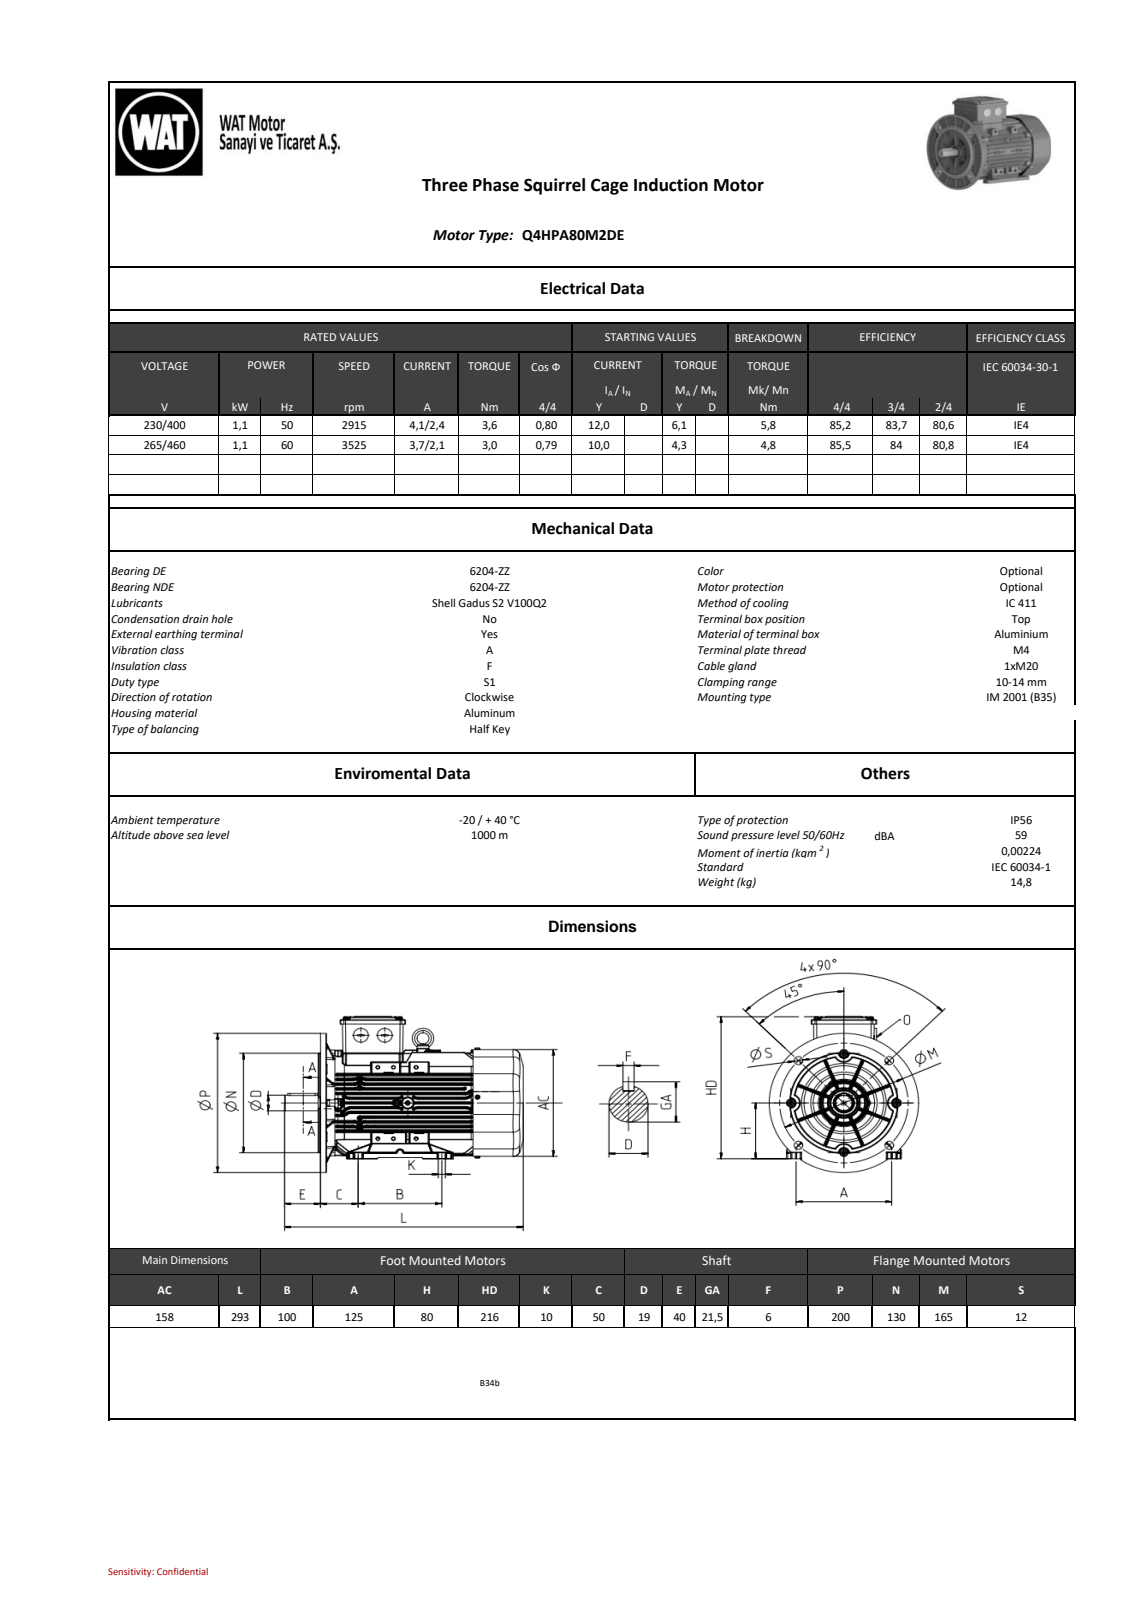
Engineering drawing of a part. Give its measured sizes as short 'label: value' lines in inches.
name: model1
written by: SIEMENS PLM Software NX2206.8101 (AUTOMOTIVE_DESIGN)
unit: in
bodies: 0 solids, 6406 faces (1209 planar, 1769 cylindrical, 3428 other)
size: 11.535 × 9.272 × 7.874
holes: 3× ⌀0.118, 2× ⌀0.138, 2× ⌀0.181, 2× ⌀0.197, 1× ⌀0.315, 1× ⌀2.244
bosses: 5× ⌀0.236, 2× ⌀0.842, 2× ⌀0.328, 1× ⌀5.768, 1× ⌀5.118, 1× ⌀2.402, 1× ⌀1.181, 1× ⌀0.948
rounds: 509× R0.02, 308× R0.039, 286× R0.031, 23× R0.079, 19× R0.059, 15× R0.197, 8× R0.049, 8× R2.982
face distances: 0.039, 1.652, 0.161, 0.408, 6.181, 6.18, 0.317, 0.156, 3.386, 2.06
hole spacings: 1.004, 1.739, 1.739, 1.98, 2.144, 2.793
